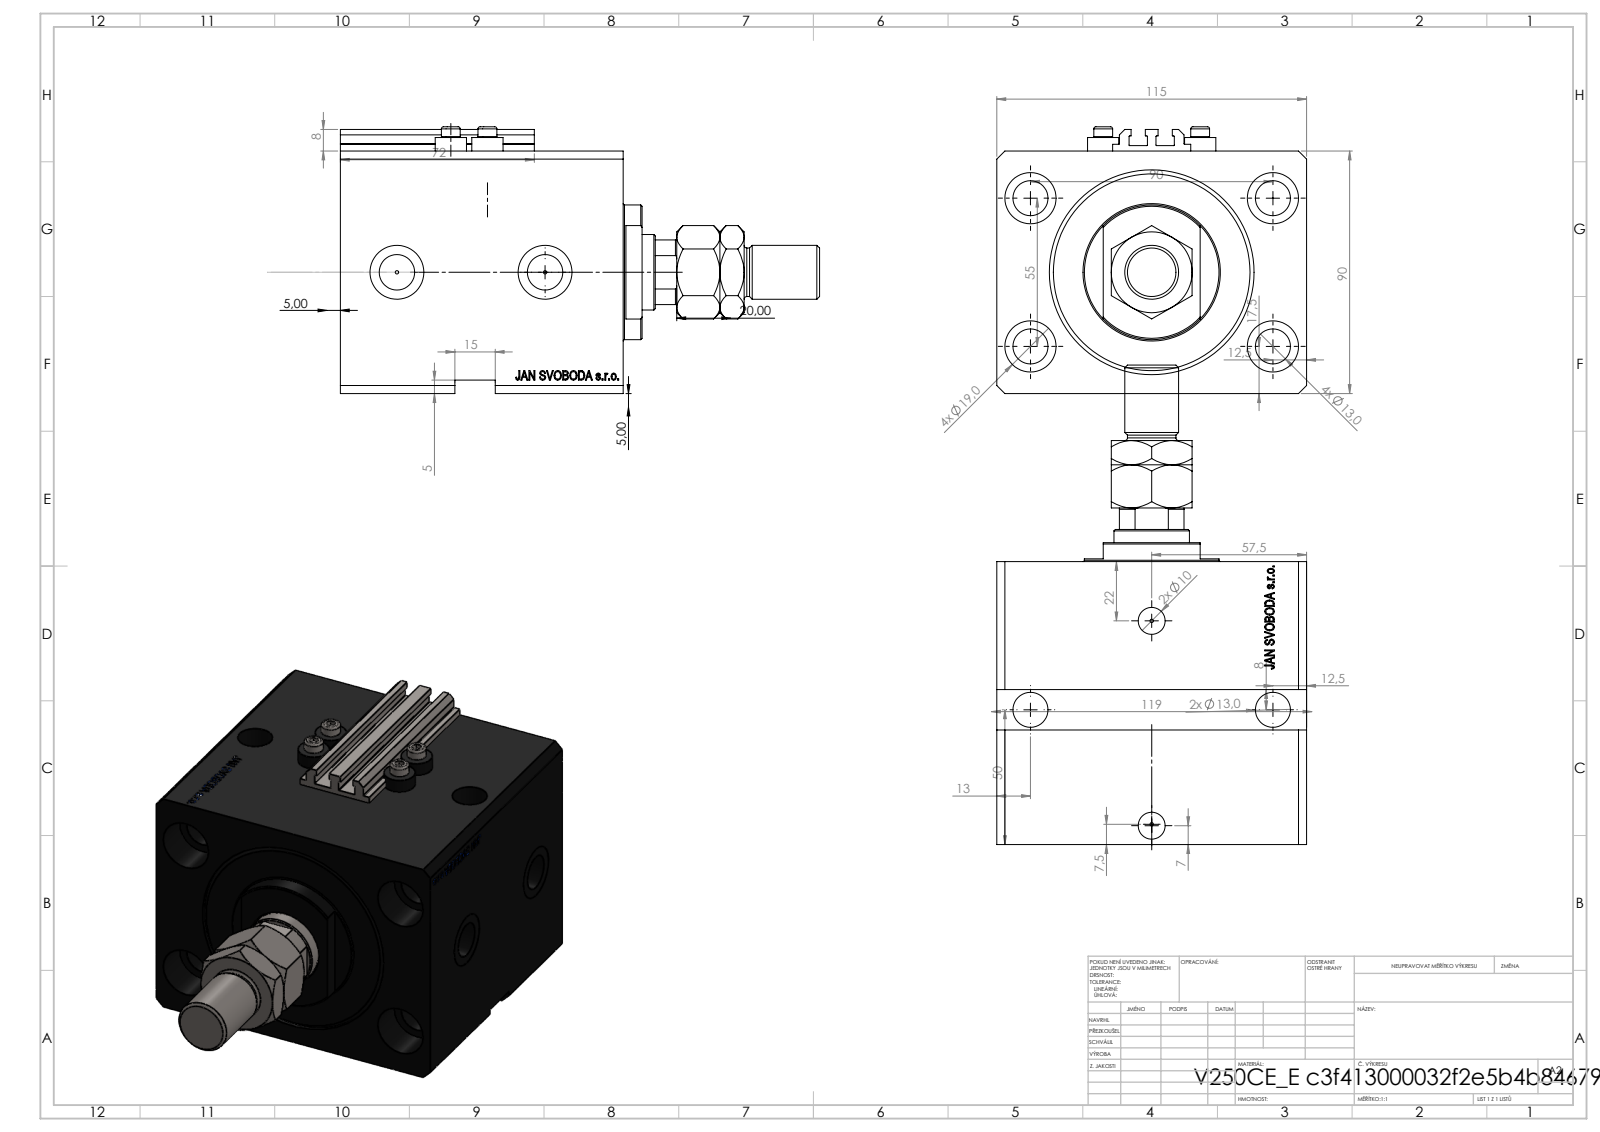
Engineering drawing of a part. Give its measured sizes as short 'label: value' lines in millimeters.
name: V250CE_E_Body; ALLEN BOLT V250CE; V250CE_C_VCP; V250CE_VC_E (+1 more)
written by: SolidWorks 2019 (CONFIG_CONTROL_DESIGN)
unit: mm
bodies: 9 solids, 1172 faces (562 planar, 142 cylindrical, 468 other)
size: 177.9 × 115 × 99
volume: 978 811 mm³; area: 163 507 mm²
holes: 6× ⌀13, 4× ⌀1.25, 4× ⌀4, 4× ⌀19, 2× ⌀10, 2× ⌀13.16, 2× ⌀20, 1× ⌀18.5, 1× ⌀28, 1× ⌀63, 1× ⌀76
bosses: 4× ⌀11.6, 4× ⌀7, 1× ⌀50, 1× ⌀20, 1× ⌀18
rounds: 10× R0.2, 1× R13.5
face distances: 90, 115, 105, 87.1, 17.9, 57, 74.9, 30.1, 20, 54.9
hole spacings: 52.74, 55, 90, 13.6, 27.39, 28.46, 33.62, 36
